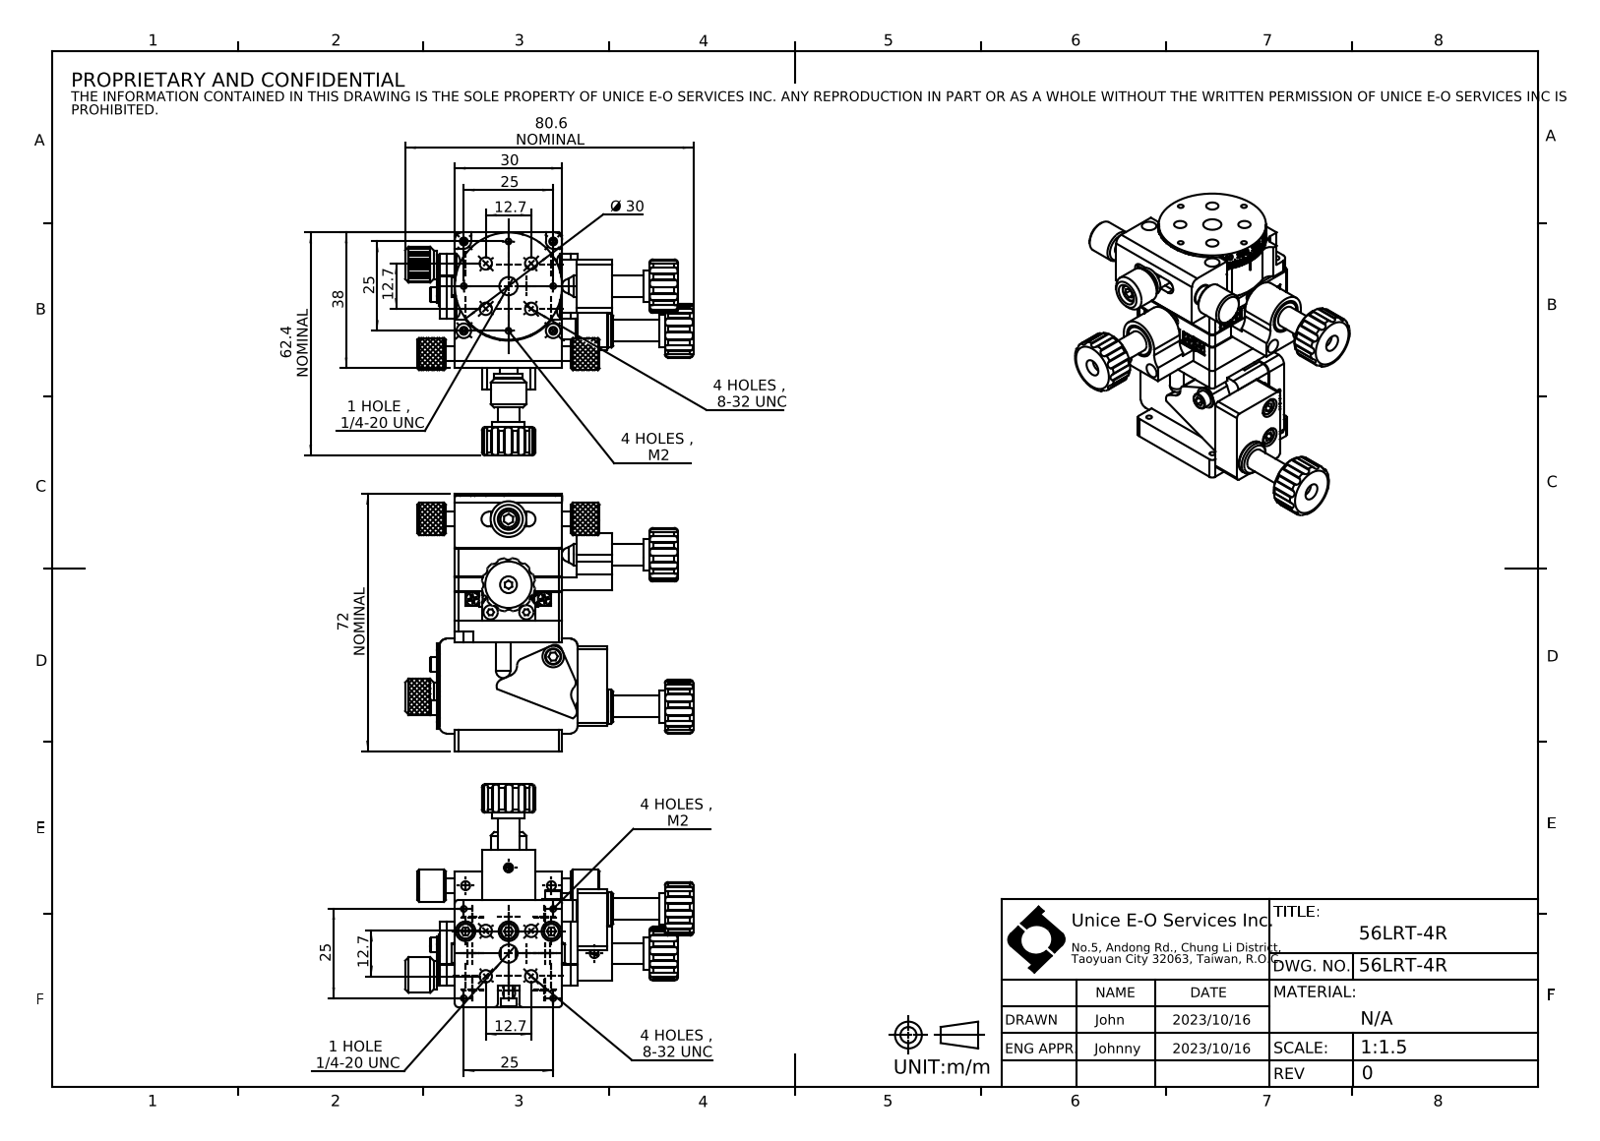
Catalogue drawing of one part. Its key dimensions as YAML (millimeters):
part_name: "56LRT-4R"
step_written_by: "SolidWorks 2022 (CONFIG_CONTROL_DESIGN)"
units: millimeters
bodies: {solids: 0, faces: 1294, planar: 734, cylindrical: 397, other: 163}
overall_size: [80.6, 72, 62.4]
round_holes:
  - {diameter: 2.5, count: 10}
  - {diameter: 1.6, count: 8}
  - {diameter: 2.05, count: 7}
  - {diameter: 5.5, count: 5}
  - {diameter: 3.45, count: 4}
  - {diameter: 4, count: 4}
  - {diameter: 6, count: 4}
  - {diameter: 4.7, count: 3}
  - {diameter: 9.5, count: 3}
  - {diameter: 2.2, count: 2}
  - {diameter: 2.7, count: 2}
  - {diameter: 4.1, count: 2}
round_bosses_or_shafts:
  - {diameter: 3.6, count: 8}
  - {diameter: 6, count: 5}
  - {diameter: 4.5, count: 5}
  - {diameter: 4, count: 5}
  - {diameter: 9, count: 4}
  - {diameter: 10, count: 2}
  - {diameter: 8, count: 2}
  - {diameter: 30, count: 1}
partial_cylinders:
  - {radius: 0.3, count: 72}
  - {radius: 1.5, count: 36}
  - {radius: 2, count: 15}
  - {radius: 1, count: 10}
  - {radius: 0.5, count: 4}
  - {radius: 2.05, count: 4}
  - {radius: 2.5, count: 4}
  - {radius: 5, count: 4}
face_to_face_distances: [6, 24, 30, 8.3, 3.9, 4.3, 18, 25.5, 4.4, 4.2]
hole_center_spacings: [12.5, 8.84, 17.68, 19.83, 19.89, 27.95, 18.76, 25]
